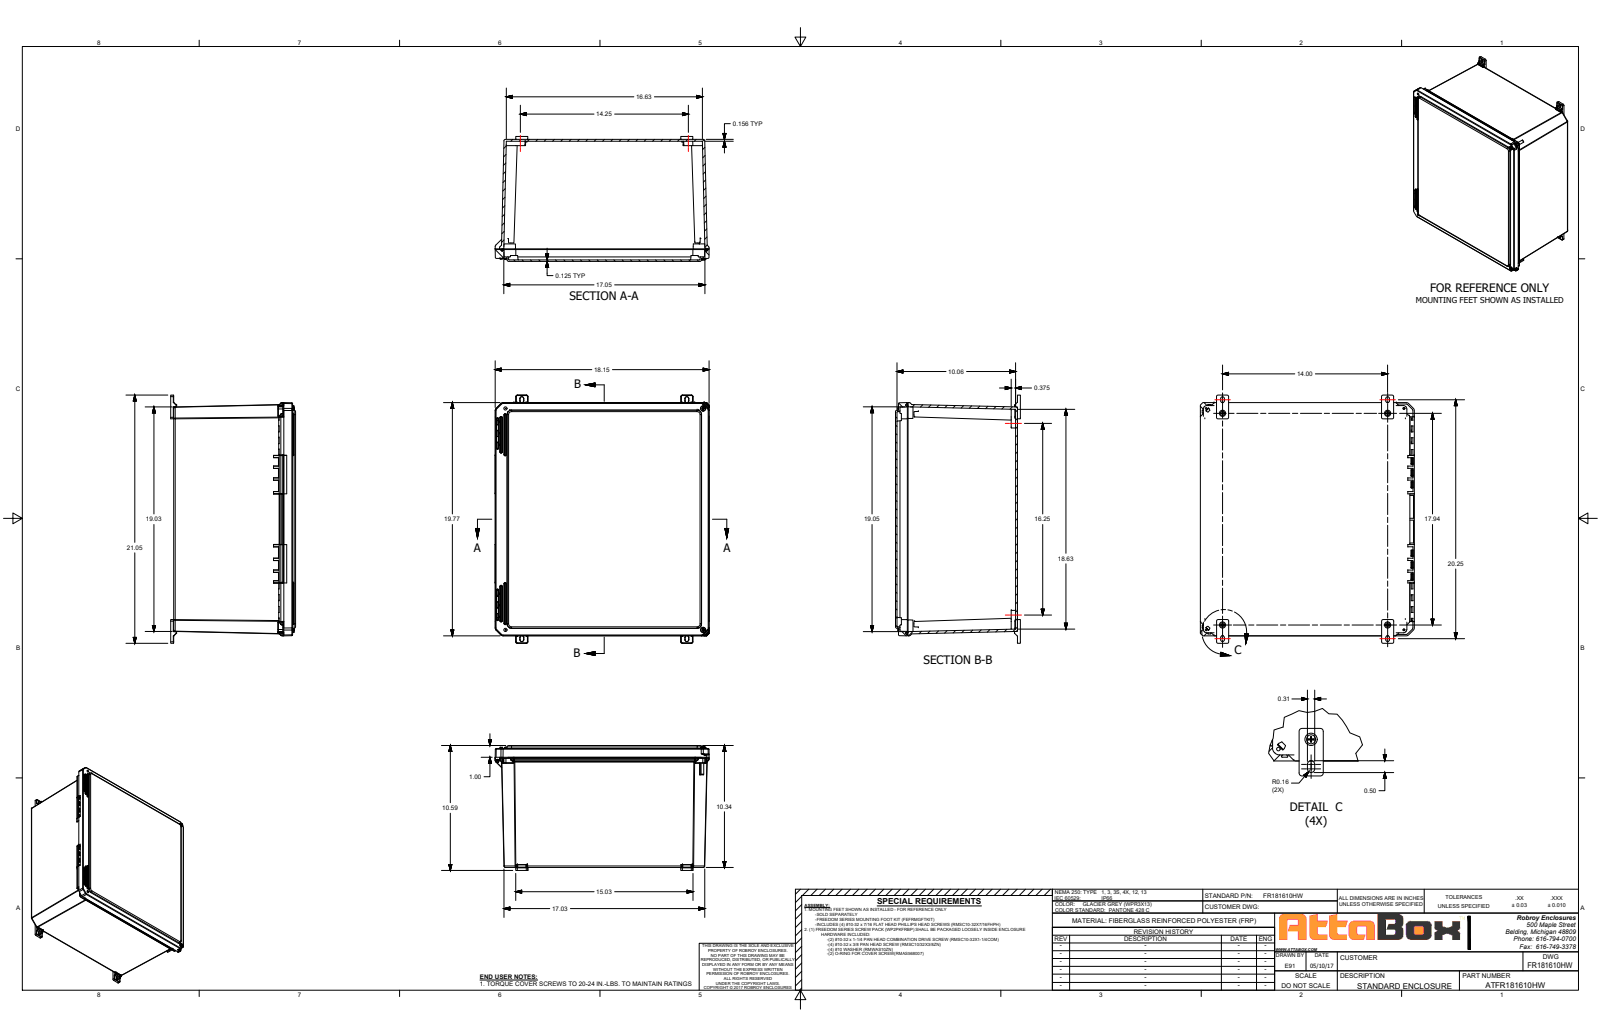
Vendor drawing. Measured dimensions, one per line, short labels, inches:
name: FR181610HW
written by: SolidWorks 2021 (AUTOMOTIVE_DESIGN)
unit: in
bodies: 8 solids, 2158 faces (674 planar, 837 cylindrical, 647 other)
size: 19.773 × 18.147 × 10.341
volume: 258.8 in³; area: 2 938 in²
holes: 8× ⌀0.152, 4× ⌀0.252, 4× ⌀0.253, 2× ⌀0.219, 2× ⌀0.227, 2× ⌀0.313, 1× ⌀0.137, 1× ⌀0.15
bosses: 2× ⌀0.45, 2× ⌀0.435, 2× ⌀0.199, 1× ⌀0.209, 1× ⌀0.135
rounds: 171× R0.01, 88× R0.005, 49× R0.02, 45× R0.03, 24× R0.03, 24× R0.09, 24× R0.096, 22× R0.125
face distances: 0.125, 0.156, 10.341, 10.185, 0.2, 10.216, 10.06, 0.202, 0.202, 0.25
hole spacings: 17.555, 18.409, 1.783, 23.392, 0.856, 15.562, 16.772, 17.097
